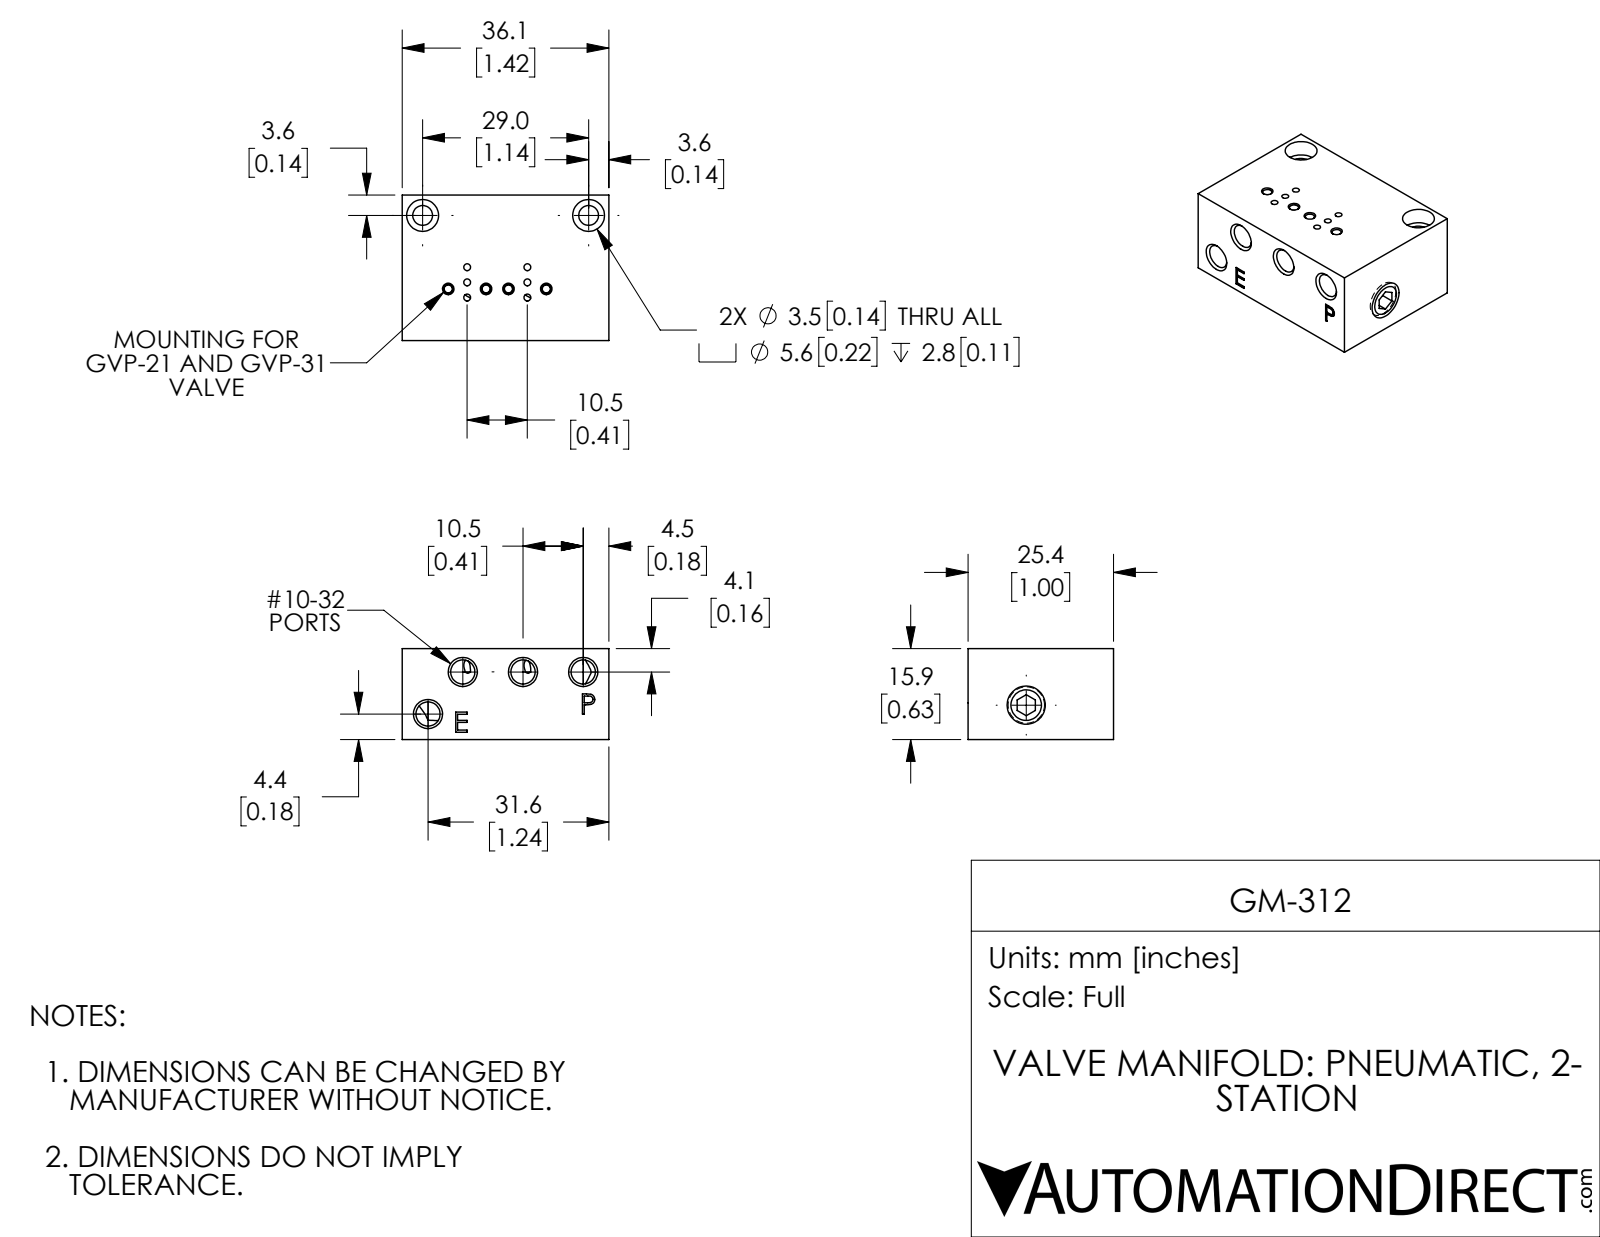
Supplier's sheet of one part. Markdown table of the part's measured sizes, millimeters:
| quantity | value |
| --- | --- |
| part name | GM-312 |
| STEP written by | SolidWorks 2018 (AUTOMOTIVE_DESIGN) |
| units | millimeters |
| bodies | 3 solids, 159 faces (53 planar, 52 cylindrical, 54 other) |
| overall size | 36.1 × 25.4 × 15.9 |
| volume | 12 400 mm³ |
| surface area | 6 257 mm² |
| round holes (diameter × count) | 1.2 × 6, 1.4 × 4, 1.6 × 4, 4.2 × 4, 3.5 × 2, 5.4 × 2, 5.6 × 2 |
| round bosses / shafts (diameter × count) | 6.4 × 2 |
| main face-to-face distances | 15.9, 25.4, 36.1, 3.2, 13, 2.8, 6.4, 29.7, 4.1, 32 |
| hole center spacings | 10.5, 2.6, 5, 10.8, 3.5, 3.6, 5.3, 10.5 |
